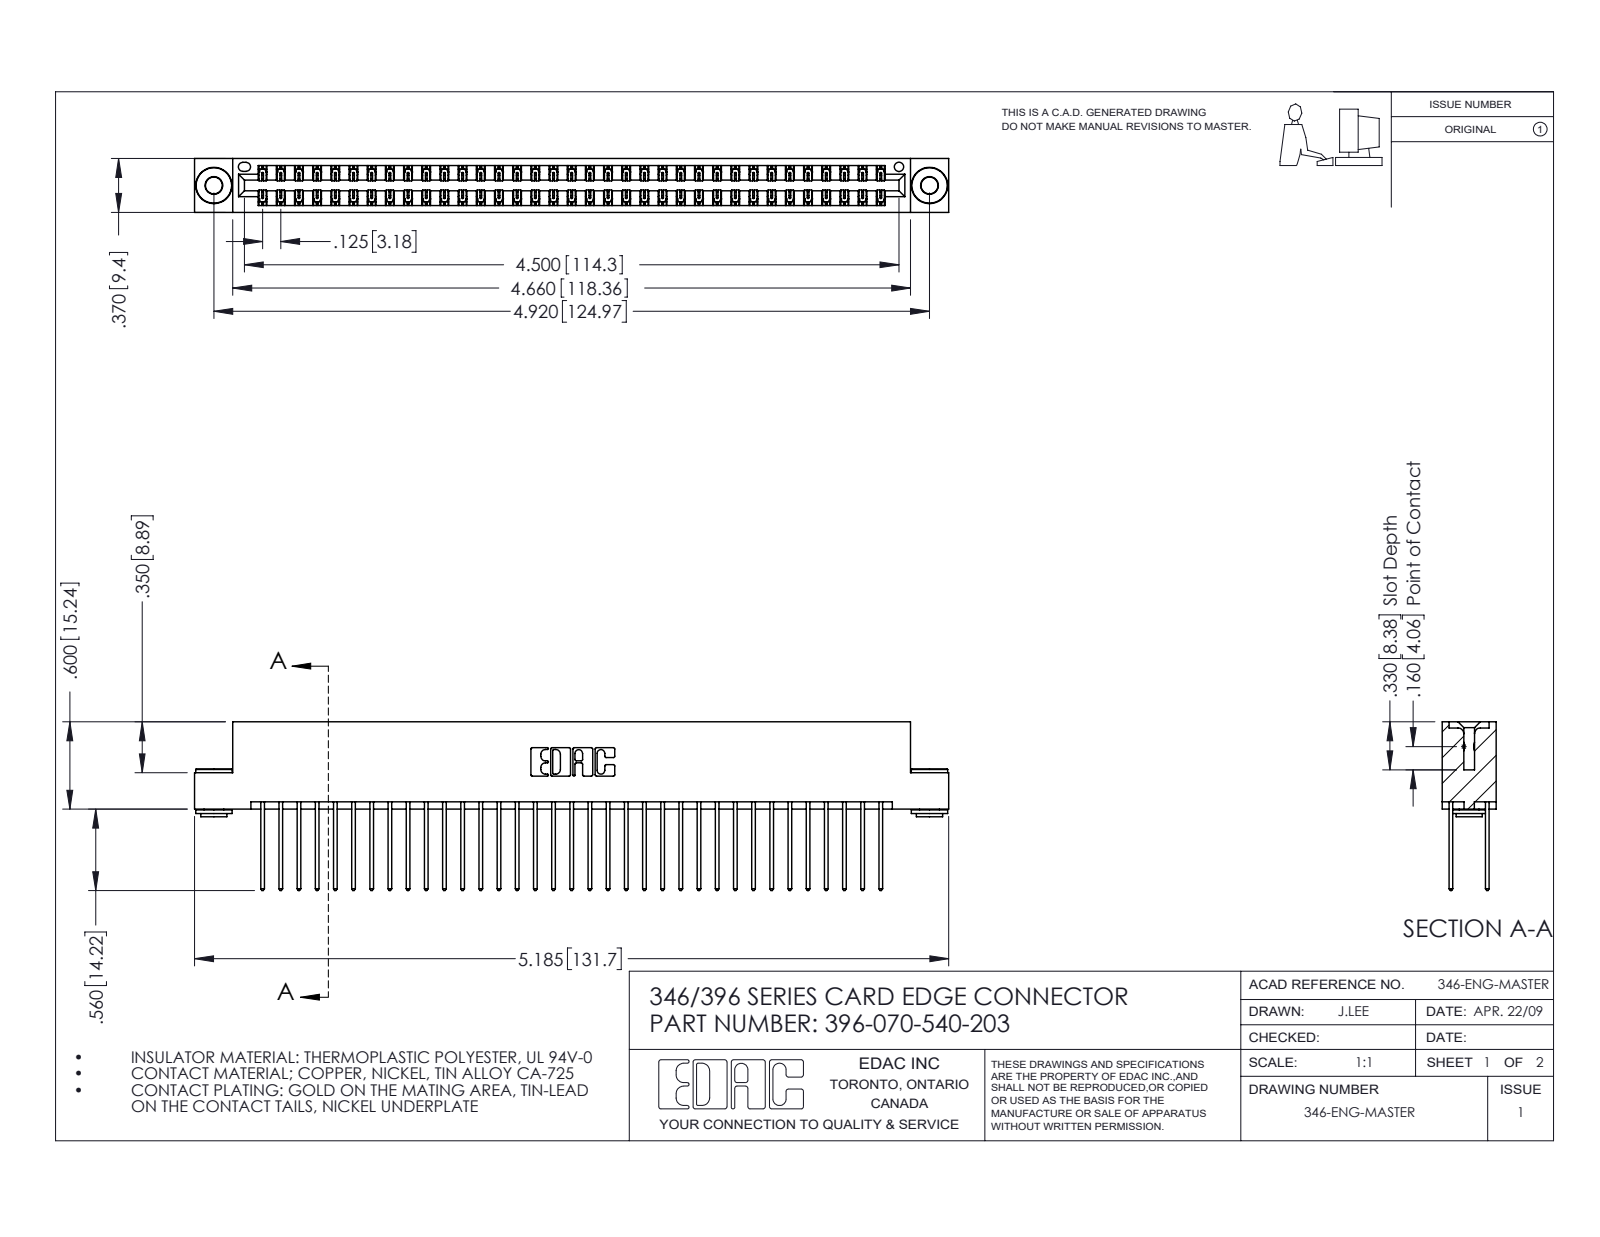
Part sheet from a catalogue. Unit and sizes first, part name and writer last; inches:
Units: inches
Overall size (bounding box): 5.185 × 1.16 × 0.37
Round holes (diameter × count): ⌀0.116 ×2, ⌀0.156 ×2, ⌀0.064 ×1
Round bosses / shafts (diameter × count): ⌀0.25 ×2, ⌀0.18 ×2, ⌀0.136 ×2
Partial cylindrical surfaces — rounded edges, fillets, slot ends (radius × count): R0.006 ×105, R0.01 ×70, R0.01 ×22, R0.007 ×6, R0.031 ×6, R0.026 ×3, R0.014 ×2, R0.022 ×2
Main face-to-face distances: 0.048, 0.322, 0.25, 0.025, 0.072, 0.298, 0.37, 0.275, 0.148, 0.222
Hole centre spacings: 0.246, 4.711, 4.92
Volume: 0.798 in³ · Surface area: 29.96 in²
Bodies: 73 solids, 3800 faces (2536 planar, 1256 cylindrical, 8 other)
Part name (STEP PRODUCT): 345-250-002_345-250-002-102; 345-292-001_345-293-140; 396-070-540-203; 346 Part_Flush Mounting Lugs - 0.156 Dia-TH
STEP written by: SolidWorks 2016 (CONFIG_CONTROL_DESIGN)
